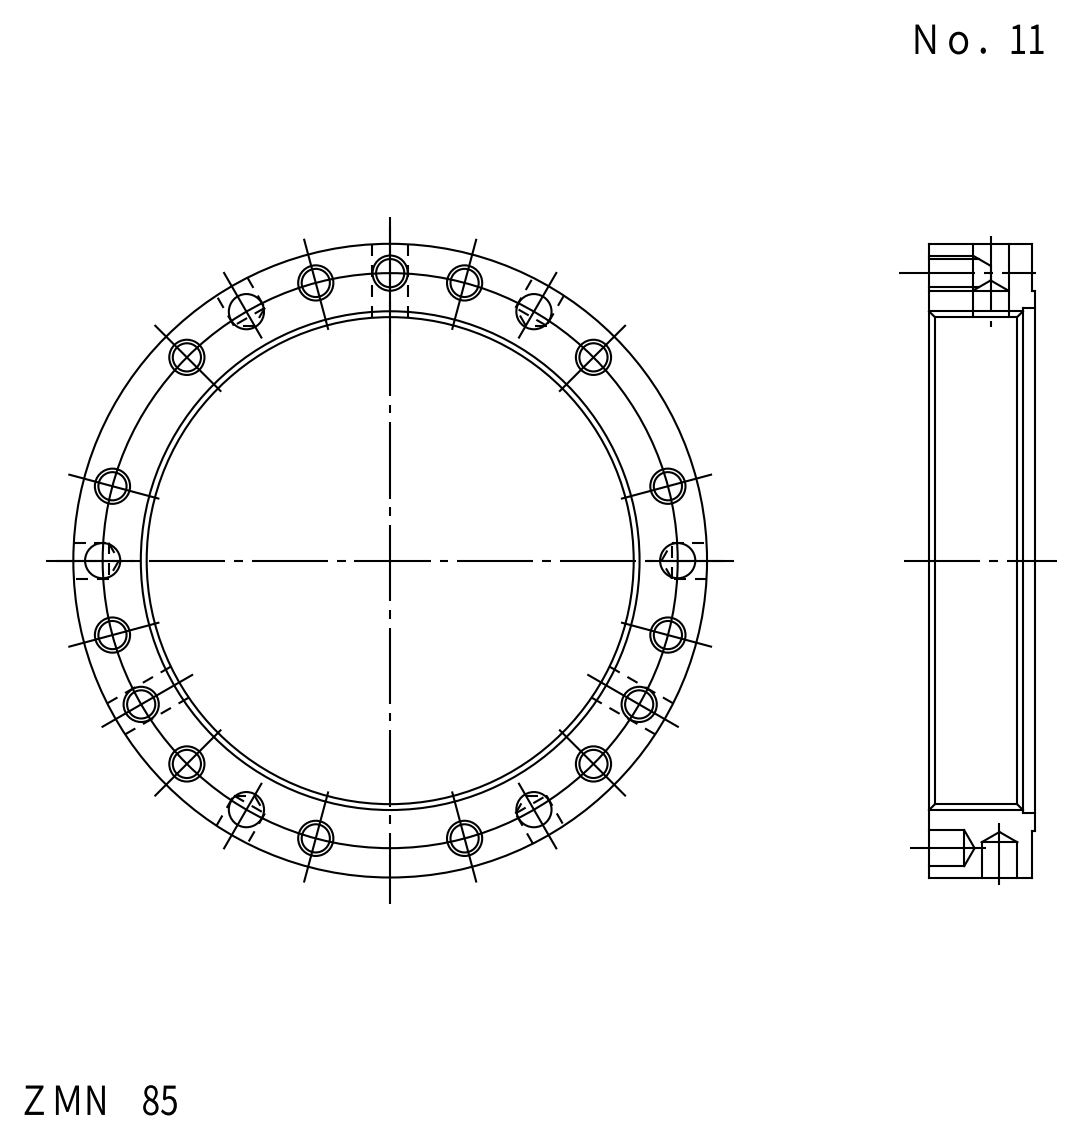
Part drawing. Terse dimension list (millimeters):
name: FKD ZMN85
written by: Autodesk Inventor LT (CONFIG_CONTROL_DESIGN)
unit: mm
bodies: 1 solid, 62 faces (4 planar, 34 cylindrical, 24 other)
size: 108 × 108 × 18
volume: 54 917 mm³; area: 22 115 mm²
holes: 14× ⌀4.92, 12× ⌀6.1, 1× ⌀4.92, 1× ⌀85, 1× ⌀86
bosses: 1× ⌀108, 1× ⌀92
face distances: 17.5, 0.5, 18, 1.5, 1, 16.5
hole spacings: 49, 12.79, 59.66, 69.3, 84.87, 90.54, 37.5, 77.75
